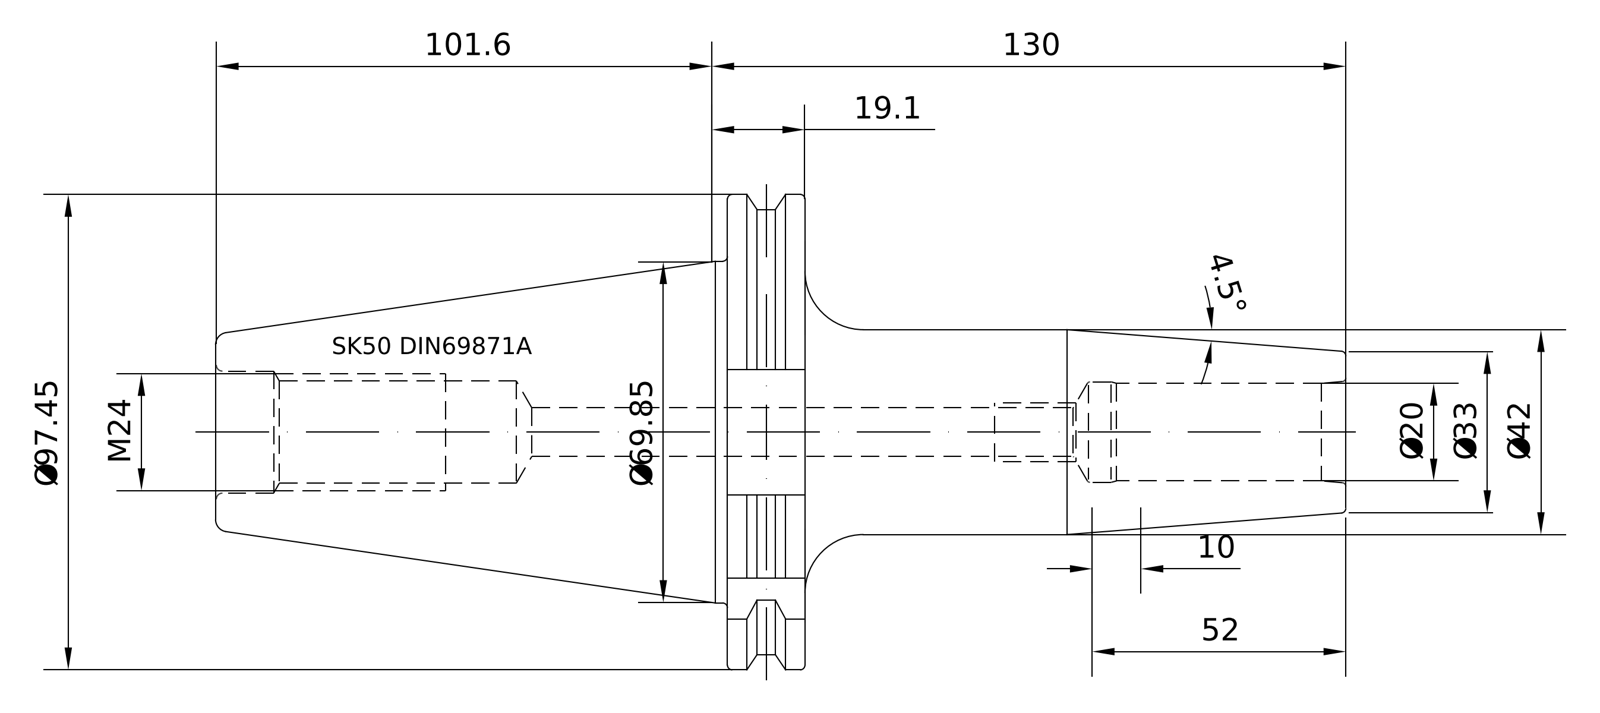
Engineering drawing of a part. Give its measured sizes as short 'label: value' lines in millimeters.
name: 50-444-20
written by: PRO/ENGINEER BY PARAMETRIC TECHNOLOGY CORPORATION, 2010430 (CONFIG_CONTROL_DESIGN)
unit: mm
bodies: 1 solid, 93 faces (21 planar, 24 cylindrical, 48 other)
size: 231.6 × 97.47 × 94
volume: 465 530 mm³; area: 58 578 mm²
holes: 1× ⌀20, 1× ⌀20.75, 1× ⌀25.01, 1× ⌀25.7
bosses: 1× ⌀91, 1× ⌀69.15, 1× ⌀42, 1× ⌀24.01
rounds: 1× R1.75, 1× R48.74
face distances: 15.85, 126.8, 110.95, 72.8, 104.8, 120.65, 231.6, 179.6, 74.8, 58.95
